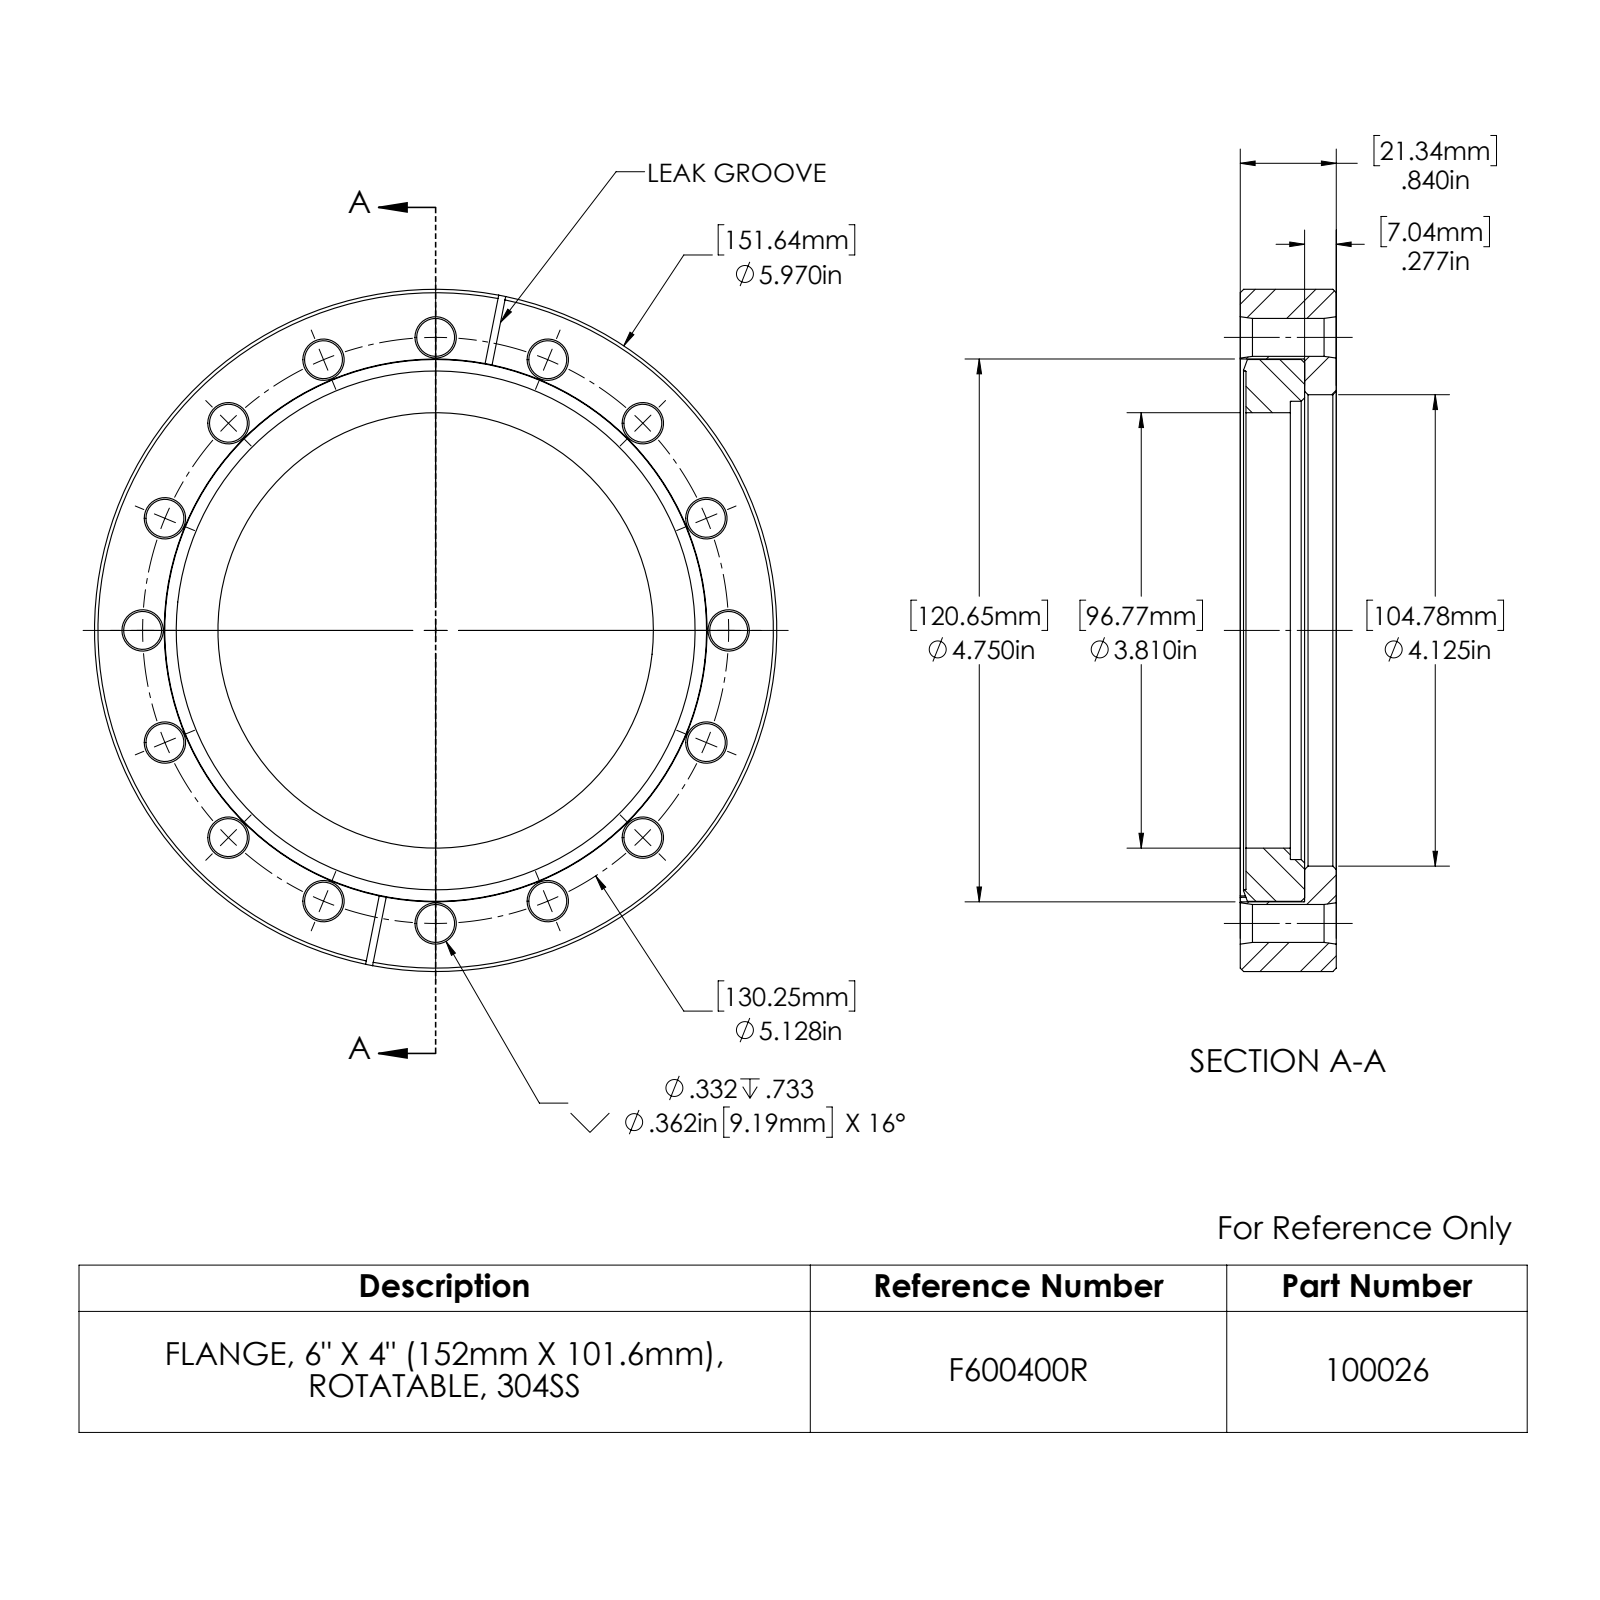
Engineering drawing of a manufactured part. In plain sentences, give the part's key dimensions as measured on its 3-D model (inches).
The part is named "100026; 915006; 910026". Its 3-D file was written by "SolidWorks 2022 (AUTOMOTIVE_DESIGN)". It is 2 solids with 147 faces: 13 planar, 46 cylindrical and 88 other. Overall it measures 5.97 by 5.97 by 0.84 inches. Its volume is 11.66 cubic inches and its surface area 92.9 square inches. Round holes: 16 of diameter 0.332, 1 of diameter 3.81, 1 of diameter 4.01, 1 of diameter 4.125, 1 of diameter 4.54, 1 of diameter 4.75. Round bosses or shafts: 1 of diameter 5.97, 1 of diameter 4.741. The main face-to-face distances are 0.277, 0.563, 0.84, 0.05, 0.513, 0.79, 0.438, 0.388, 0.125, 0.402. The hole center spacings are 4.264, 1, 4.738, 5.03, 3.626, 1.962, 1.963, 2.564.
